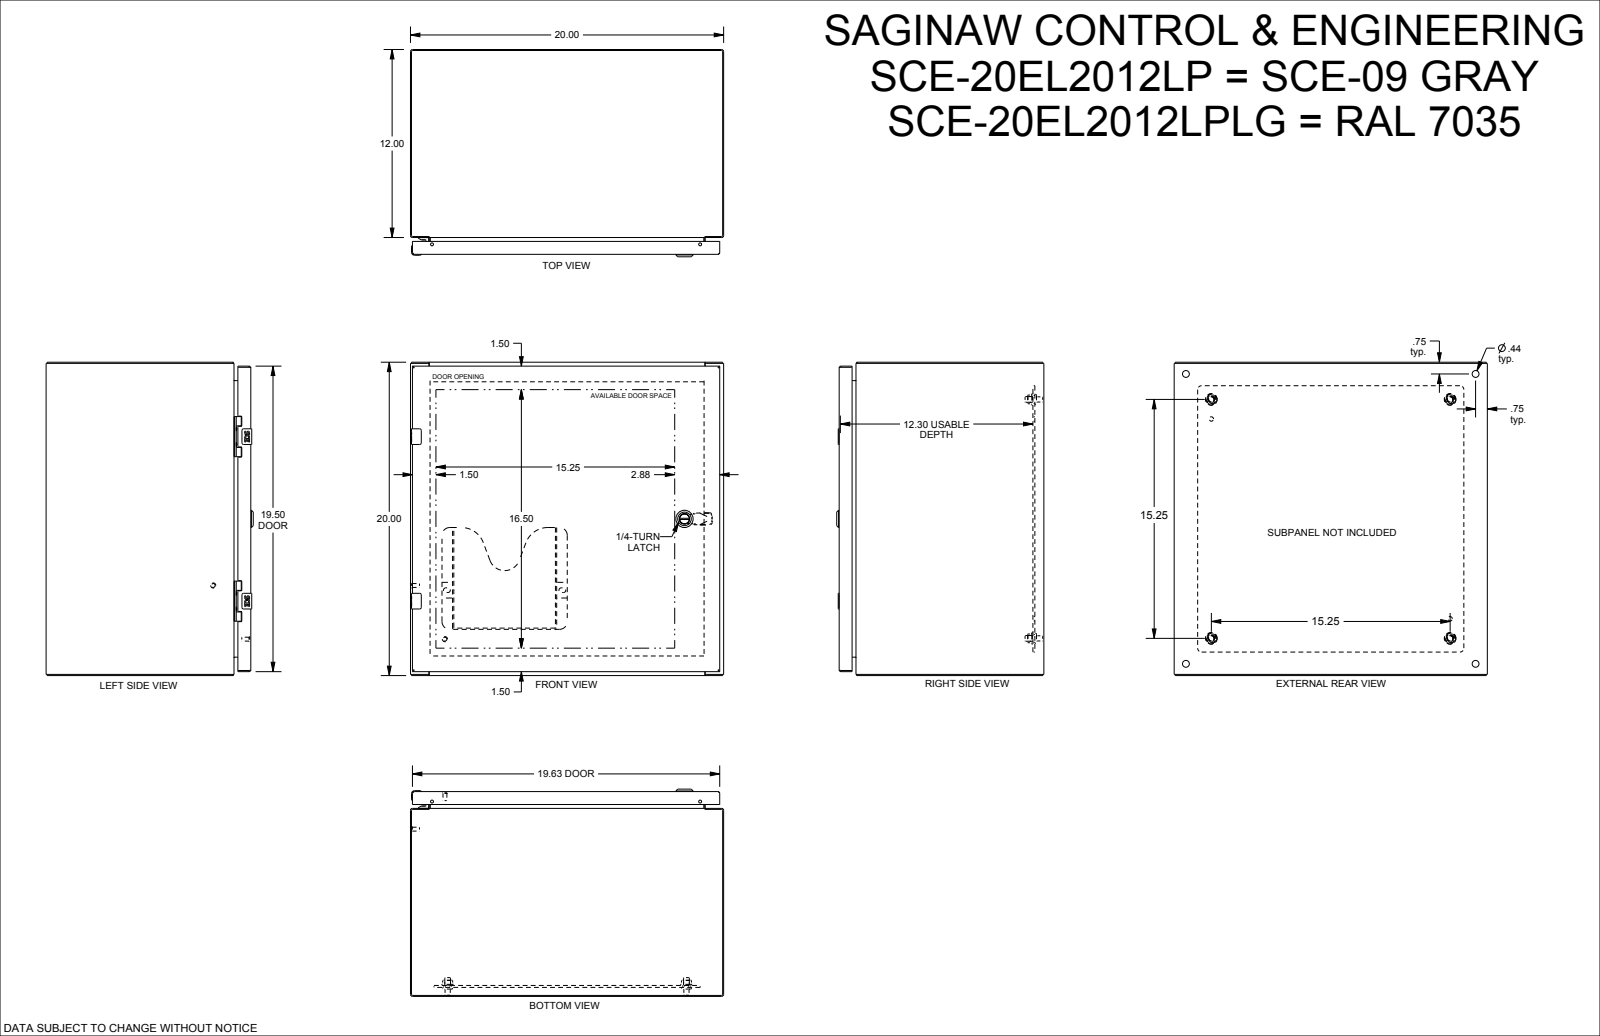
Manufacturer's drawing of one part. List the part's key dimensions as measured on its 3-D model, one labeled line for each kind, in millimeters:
Part name (STEP PRODUCT): SCE-20EL2012LP
STEP written by: SolidWorks 2021 (AUTOMOTIVE_DESIGN)
Units: millimetres
Bodies: 24 solids, 1217 faces (544 planar, 474 cylindrical, 199 other)
Overall size (bounding box): 508 × 508 × 353.9
Volume: 3 191 000 mm³ · Surface area: 3 084 000 mm²
Round holes (diameter × count): ⌀4.4 ×4, ⌀5.2 ×4, ⌀6.2 ×4, ⌀9.5 ×4, ⌀11.1 ×4, ⌀12.7 ×4, ⌀1 ×2, ⌀4.8 ×2, ⌀5.5 ×2, ⌀7.1 ×2, ⌀5 ×1, ⌀5.2 ×1
Round bosses / shafts (diameter × count): ⌀9.5 ×4, ⌀8.4 ×4, ⌀6.4 ×4, ⌀6.3 ×4, ⌀6.1 ×4, ⌀28 ×1, ⌀19.8 ×1, ⌀16 ×1
Partial cylindrical surfaces — rounded edges, fillets, slot ends (radius × count): R0.4 ×24, R1 ×17, R5.6 ×16, R1.1 ×12, R3 ×12, R0.8 ×10, R1.5 ×9, R1.6 ×8
Main face-to-face distances: 1.9, 506.1, 508, 504.2, 1.5, 330, 331.9, 330.4, 328.5, 3.2
Hole centre spacings: 12.5, 266.7, 387.4, 25, 31.8, 59.2, 59.3, 62.3
